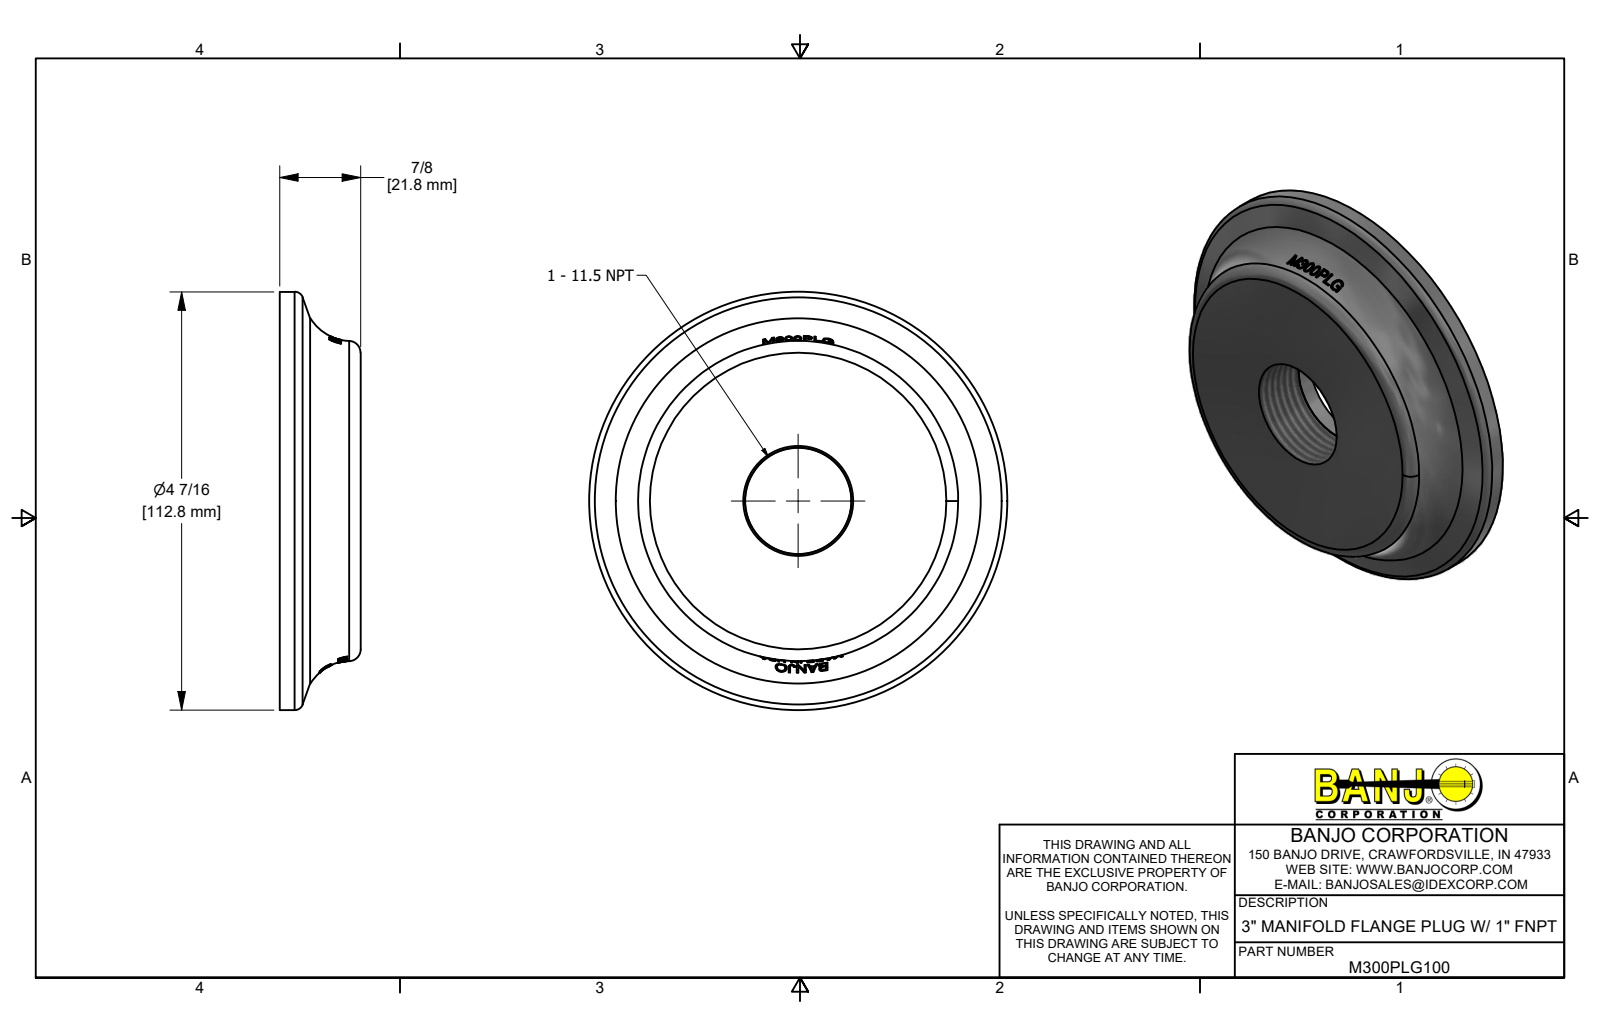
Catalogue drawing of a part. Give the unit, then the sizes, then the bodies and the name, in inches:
Units: inches
Overall size (bounding box): 4.44 × 4.44 × 0.86
Round holes (diameter × count): ⌀3 ×1, ⌀3.75 ×1
Round bosses / shafts (diameter × count): ⌀4.44 ×1, ⌀3.4 ×1
Main face-to-face distances: 0.41, 0.45, 0.86, 0.1, 0.35, 0.76, 0.324, 0.224, 0.126, 0.536
Volume: 5.626 in³ · Surface area: 43.39 in²
Bodies: 1 solid, 43 faces (5 planar, 8 cylindrical, 30 other)
Part name (STEP PRODUCT): DRAWING2
STEP written by: Mechanical Desktop 2009 (CONFIG_CONTROL_DESIGN)
